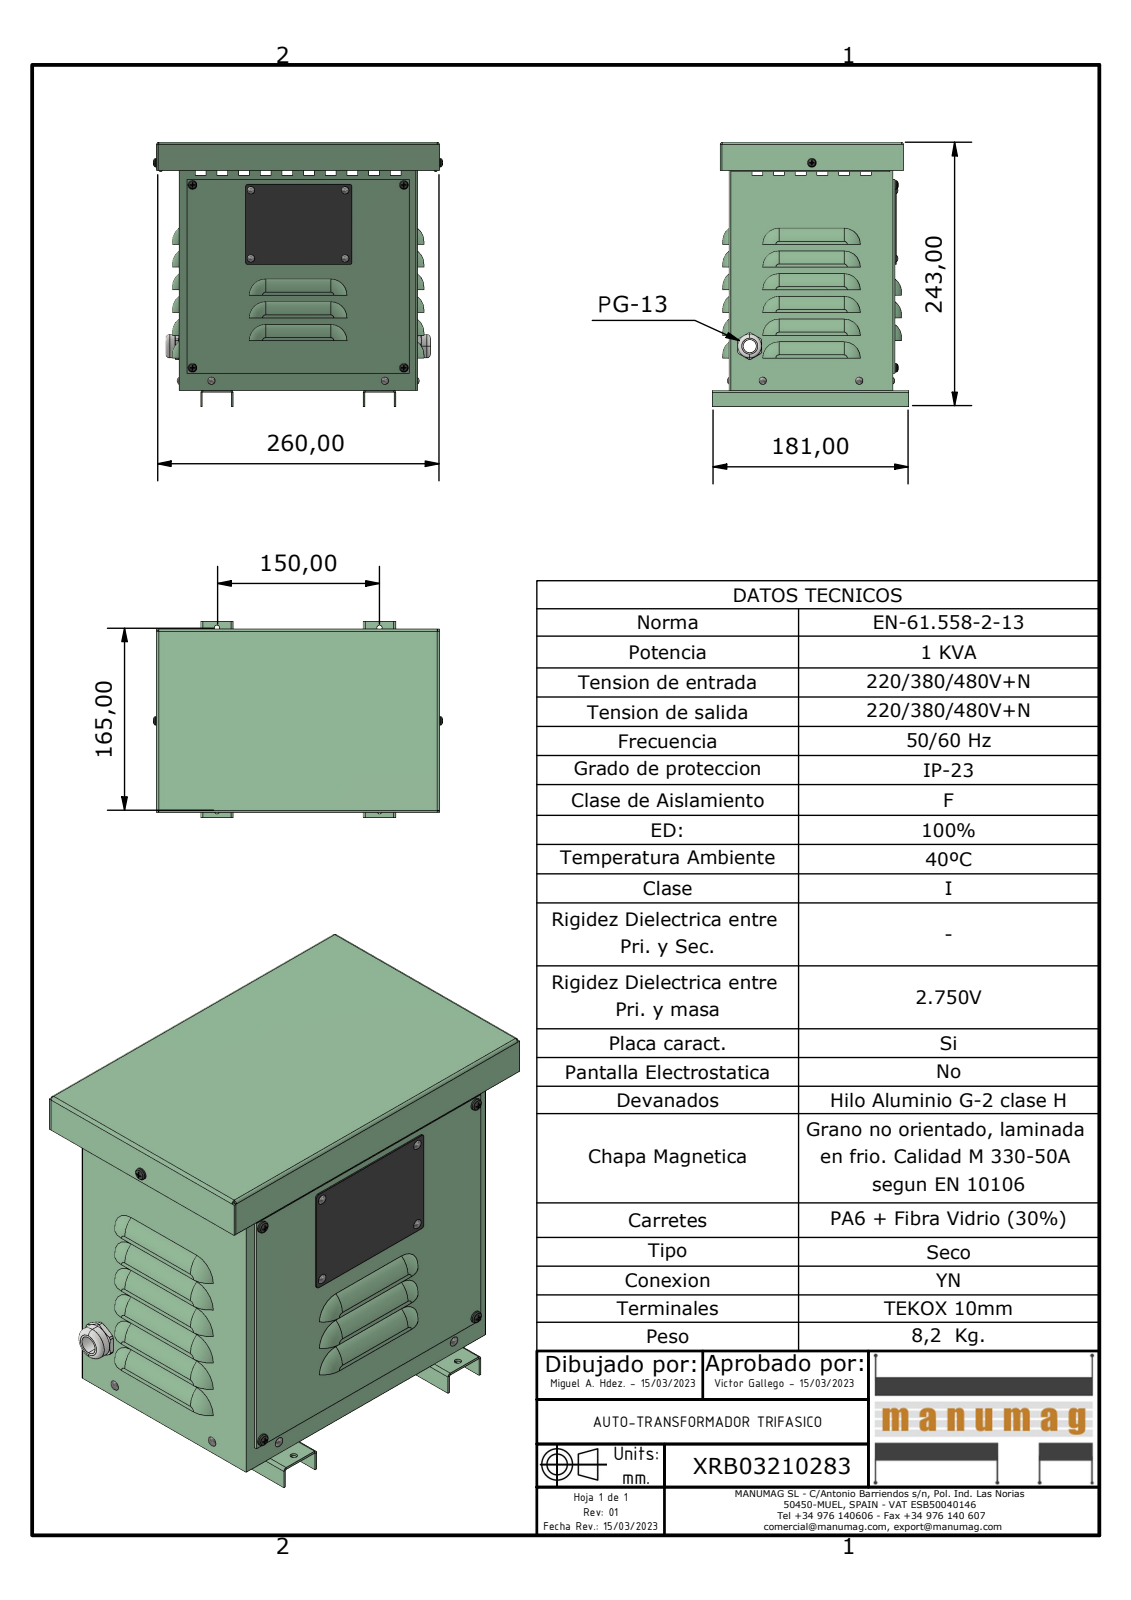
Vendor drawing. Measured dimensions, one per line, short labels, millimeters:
name: XRB03210283; JE001 - JE002 EXPORT CUERPO; JE001 - JE002 EXPORT BASE; JE001 - JE002 EXPORT PATA (+6 more)
written by: Autodesk Inventor 2023 (AUTOMOTIVE_DESIGN)
unit: mm
bodies: 27 solids, 1168 faces (639 planar, 259 cylindrical, 270 other)
size: 267.13 × 244.49 × 181
volume: 601 317 mm³; area: 669 713 mm²
holes: 13× ⌀4.8, 5× ⌀3.8, 4× ⌀3, 4× ⌀4, 1× ⌀12, 1× ⌀22
bosses: 8× ⌀3.2, 5× ⌀4, 5× ⌀3.62, 1× ⌀21.7, 1× ⌀20.4, 1× ⌀20.3, 1× ⌀18.95
rounds: 24× R14, 21× R15, 18× R4, 13× R1.5, 12× R2, 8× R0.5, 8× R2.5, 6× R14.5
face distances: 1.5, 149.5, 227.99, 218.5, 229.49, 151.5, 151, 2, 153, 217
hole spacings: 169, 150, 21.22, 26, 43.01, 50, 54.23, 63
